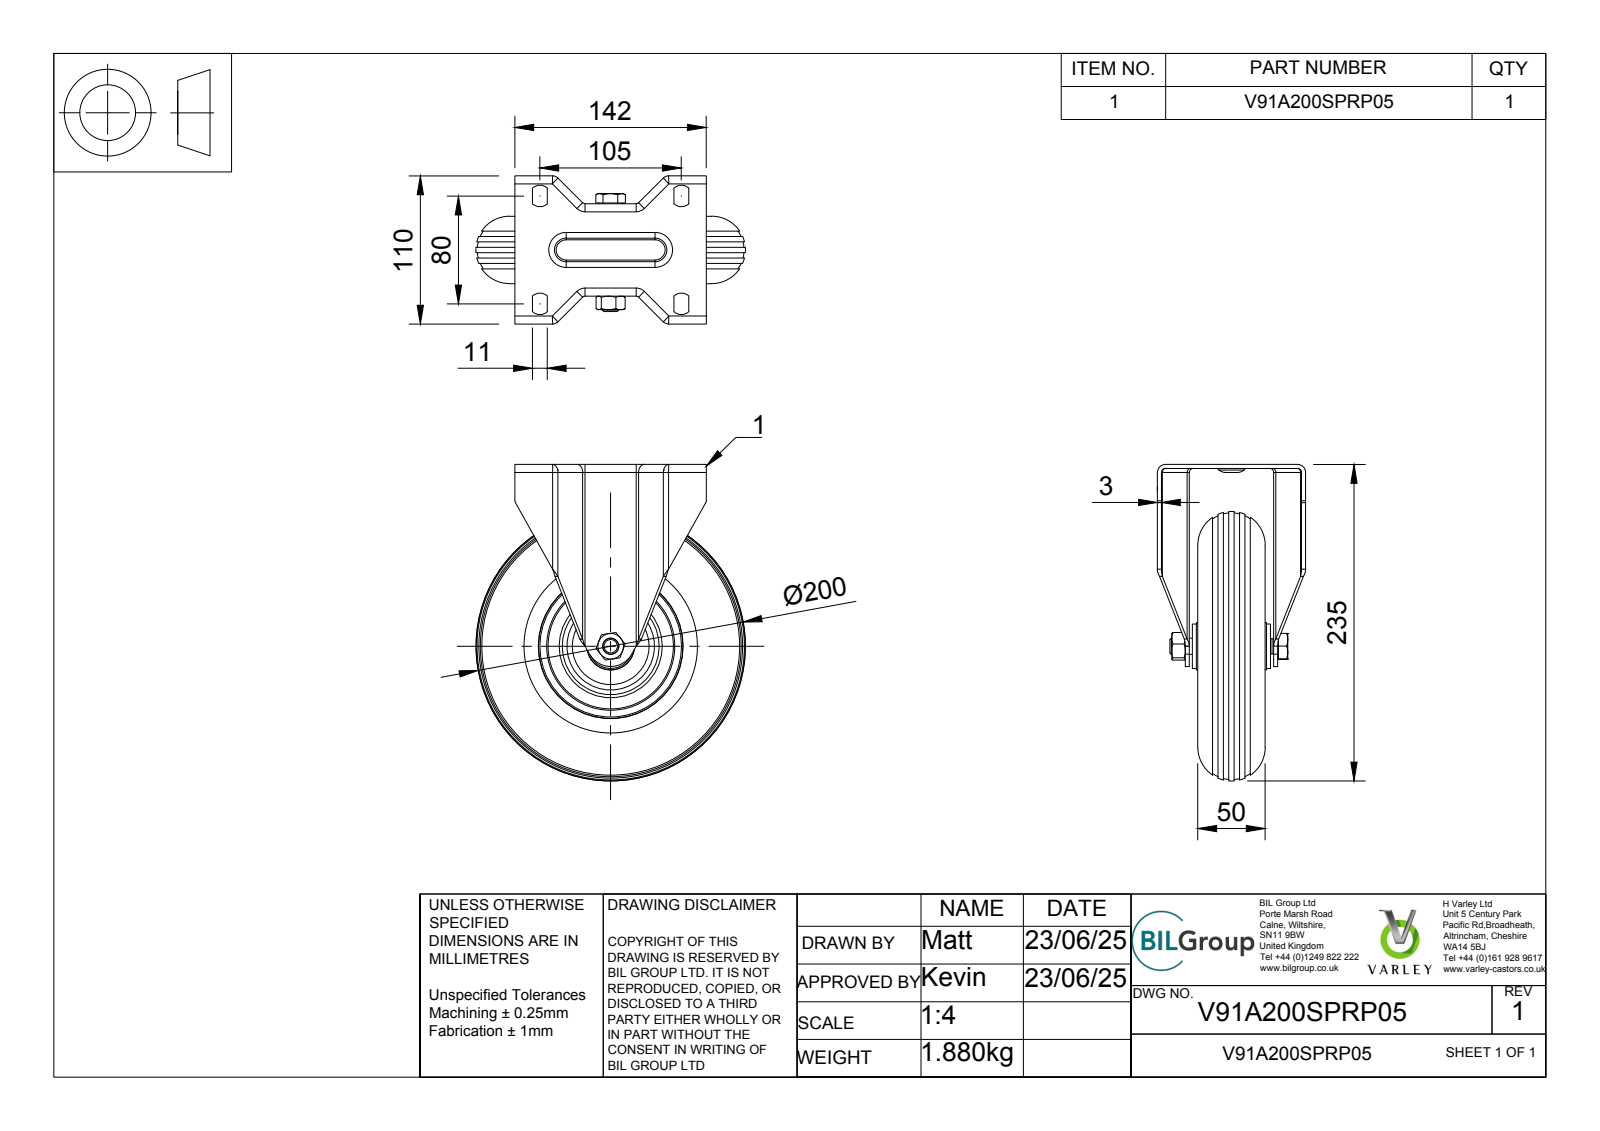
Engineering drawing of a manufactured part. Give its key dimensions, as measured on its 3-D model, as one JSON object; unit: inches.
{"part_name": "V91A200SPRP05 v2; ruota pneumatica200; nucleo; pneumatico (+6 more)", "step_written_by": "Autodesk Translation Framework v14.10.0.0 (AUTOMOTIVE_DESIGN)", "units": "inches", "bodies": {"solids": 9, "faces": 318, "planar": 128, "cylindrical": 90, "other": 100}, "overall_size": [9.252, 7.874, 4.331], "volume_in3": 26.68, "surface_area_in2": 652.8, "round_holes": [[0.398, 1], [0.488, 1], [0.827, 1], [0.866, 1], [3.976, 1]], "round_bosses_or_shafts": [[4.213, 1], [1.378, 1], [1.299, 1], [1.22, 1], [1.142, 1], [0.677, 1], [0.472, 1], [0.435, 1]], "partial_cylinders_radius": [[0.236, 12], [0.118, 10], [0.098, 8], [0.108, 8], [0.217, 8], [0.315, 4], [0.709, 1]], "face_to_face_distances": [0.118, 0.674, 2.581, 2.699, 0.816, 3.396, 3.397, 0.816, 4.213, 0.793]}
